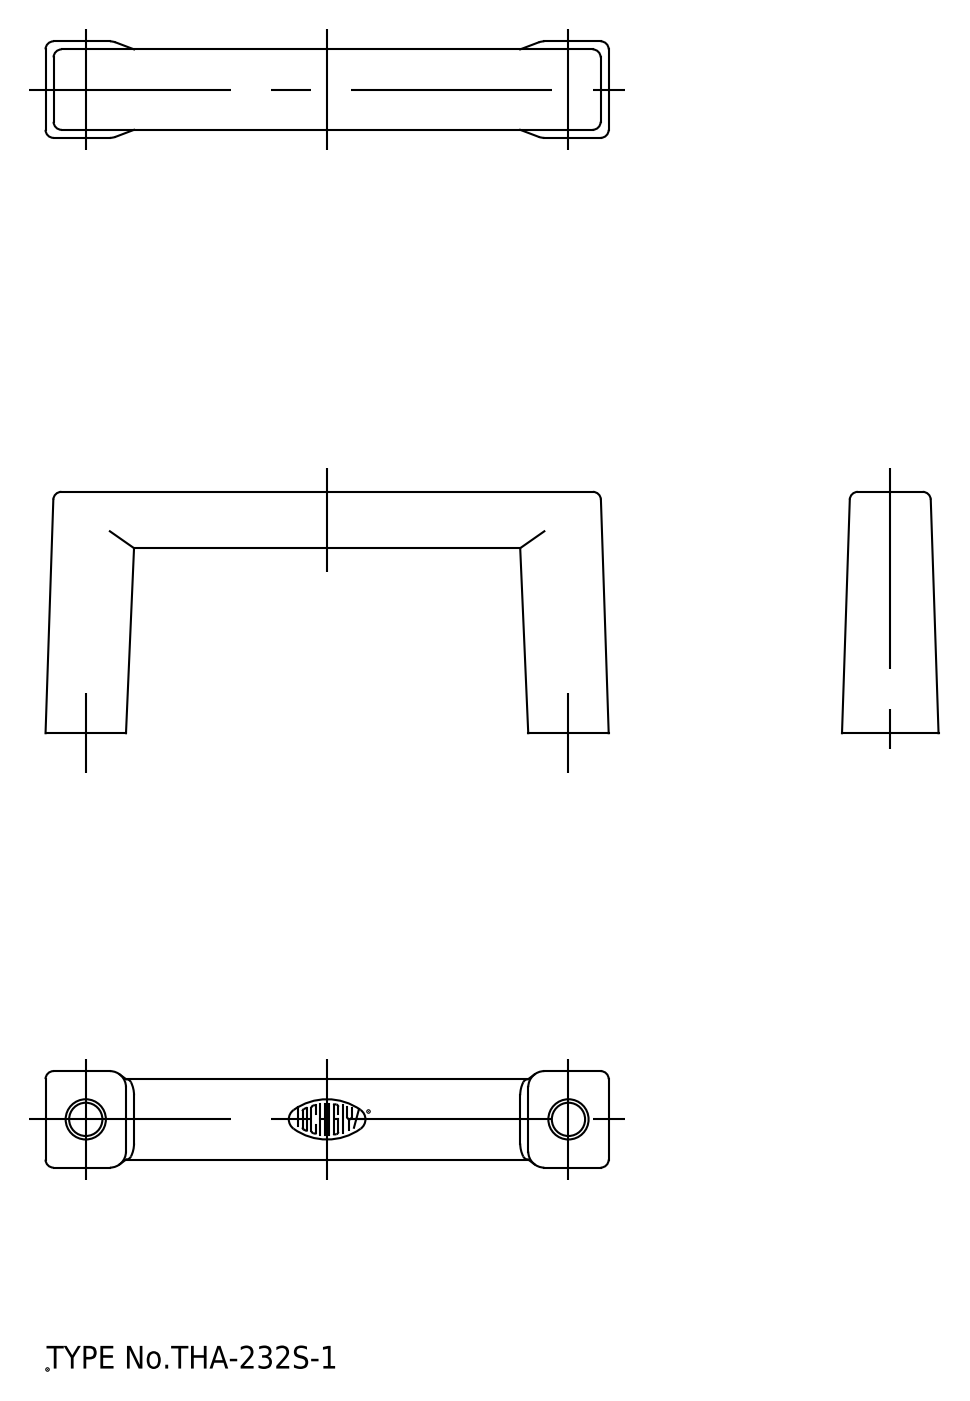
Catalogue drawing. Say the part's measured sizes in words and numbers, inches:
Its 3-D file was written by "spGate 19.8.4 (****-****-****-****) (AUTOMOTIVE_DESIGN)". It is 1 solid with 34 faces: 12 planar, 17 cylindrical and 5 other. Overall it measures 2.756 by 1.181 by 0.472 inches. Its volume is 0.575 cubic inches and its surface area 7.099 square inches. Round holes: 1 of diameter 0.197. Partial cylindrical surfaces (rounded edges, fillets, slot ends): 8 of radius 0.039, 6 of radius 0.079, 1 of radius 0.098. The main face-to-face distances are 0.276, 0.906, 1.181, 0.472, 0.433, 0.709.
